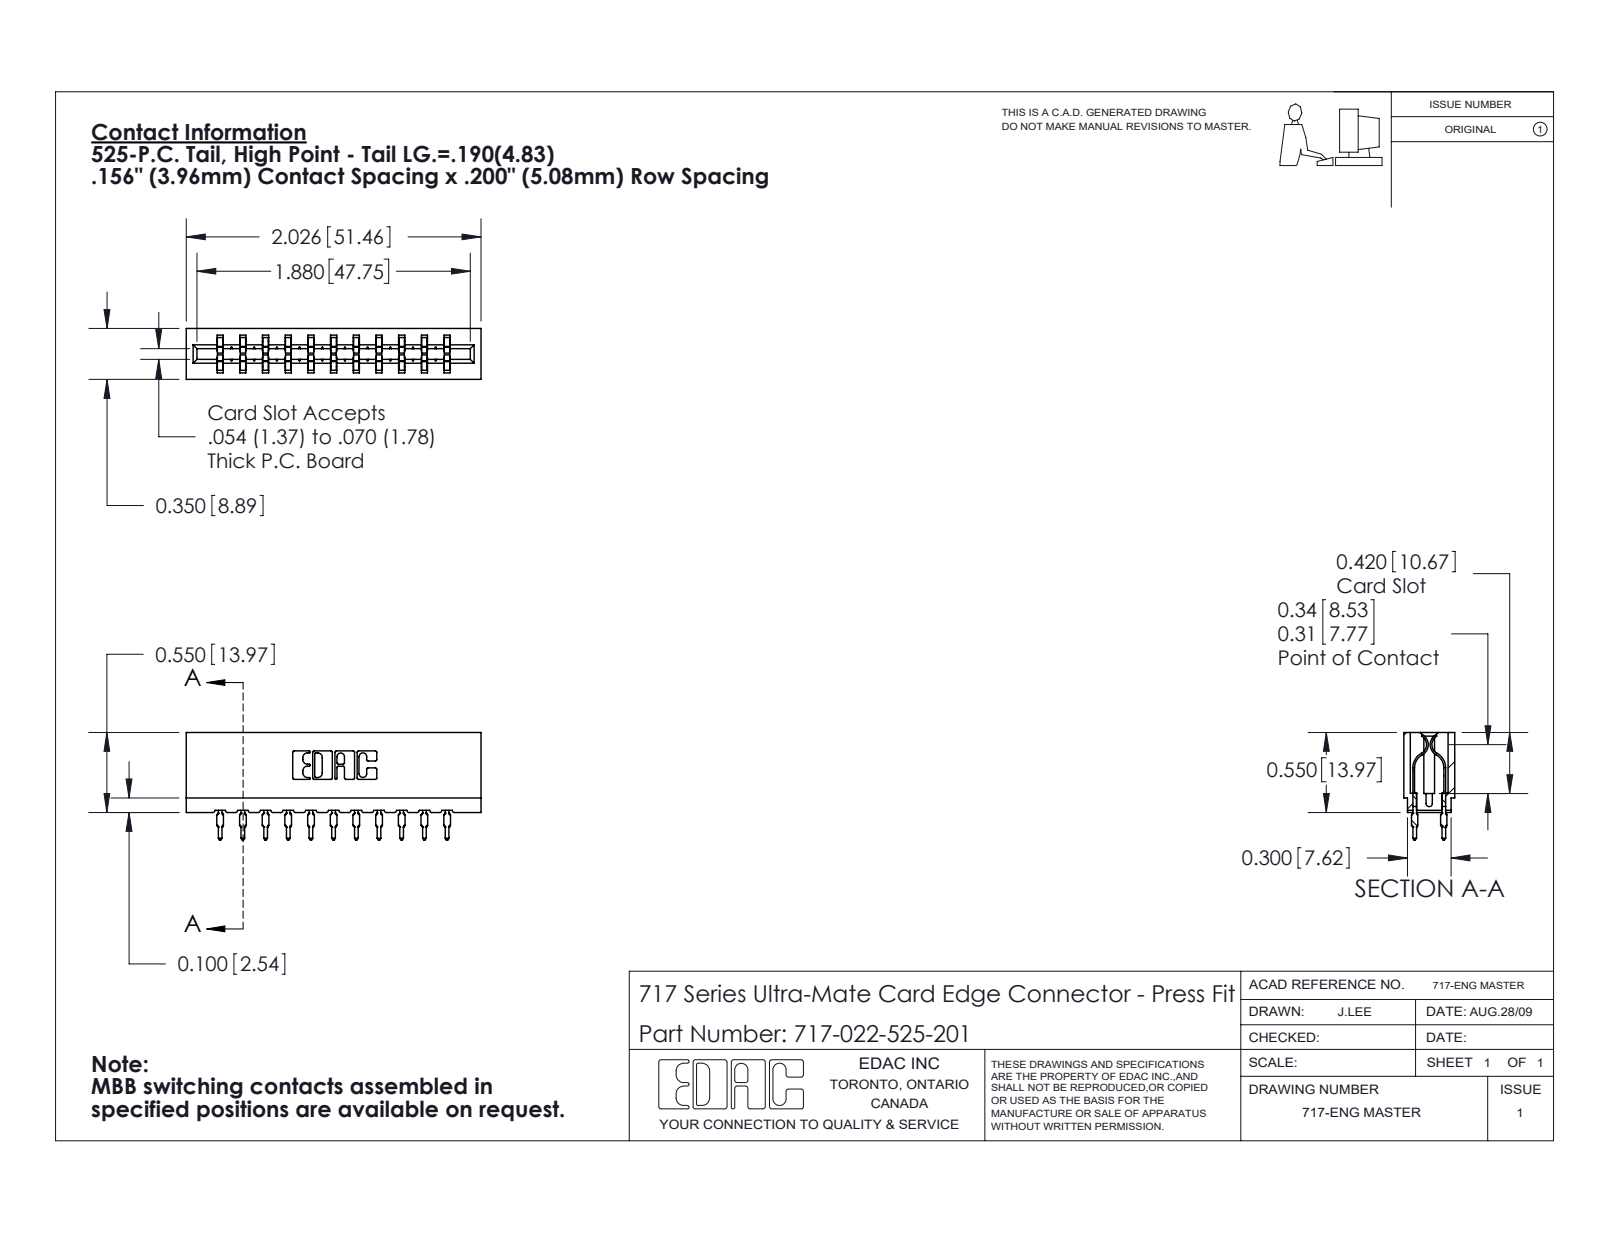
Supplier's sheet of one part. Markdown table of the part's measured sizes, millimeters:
| quantity | value |
| --- | --- |
| part name | 717 Part_Insulator Option - 06; 745-292-001_525; 717-022-525-201 |
| STEP written by | SolidWorks 2020 (CONFIG_CONTROL_DESIGN) |
| units | millimeters |
| bodies | 23 solids, 2074 faces (1077 planar, 425 cylindrical, 572 other) |
| overall size | 51.5 × 18.8 × 8.9 |
| volume | 4 590 mm³ |
| surface area | 6 568 mm² |
| partial cylindrical surfaces (radius × count) | 0.5 × 44, 0.3 × 22, 0.4 × 22, 0.1 × 8, 0.3 × 8, 0.2 × 6, 0.8 × 6, 0.7 × 3 |
| main face-to-face distances | 5.4, 4, 3.5, 11.9, 15.8, 8.9, 7.9, 5, 7.9, 1.1 |
